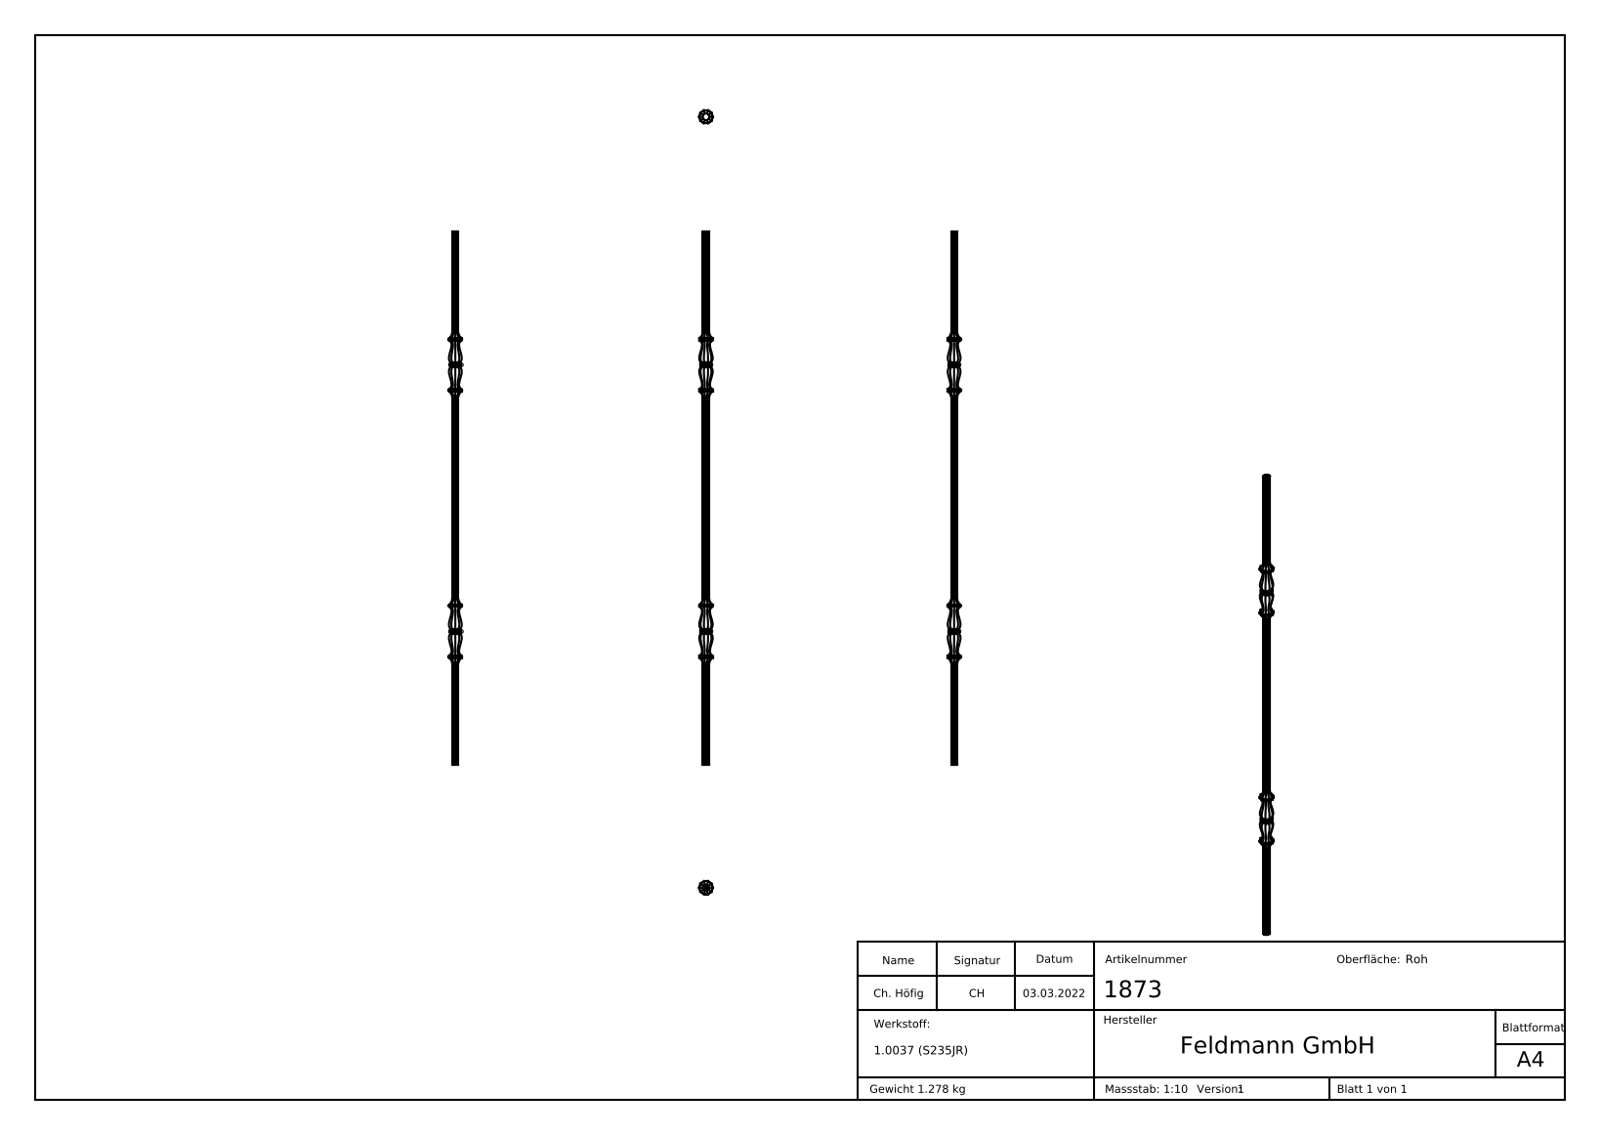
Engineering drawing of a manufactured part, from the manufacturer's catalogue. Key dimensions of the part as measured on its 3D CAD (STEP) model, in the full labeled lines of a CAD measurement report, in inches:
Part name (STEP PRODUCT): 1873
STEP written by: SolidWorks 2018 (CONFIG_CONTROL_DESIGN)
Units: inches
Bodies: 1 solid, 540 faces (201 planar, 40 cylindrical, 299 other)
Overall size (bounding box): 39.37 × 1.035 × 0.984
Volume: 10 in³ · Surface area: 71.73 in²
Partial cylindrical surfaces — rounded edges, fillets, slot ends (radius × count): R0.148 ×40
Main face-to-face distances: 0.472, 0.256, 0.728, 0.906, 0.079, 0.177, 0.65, 0.984, 0.827, 39.37
